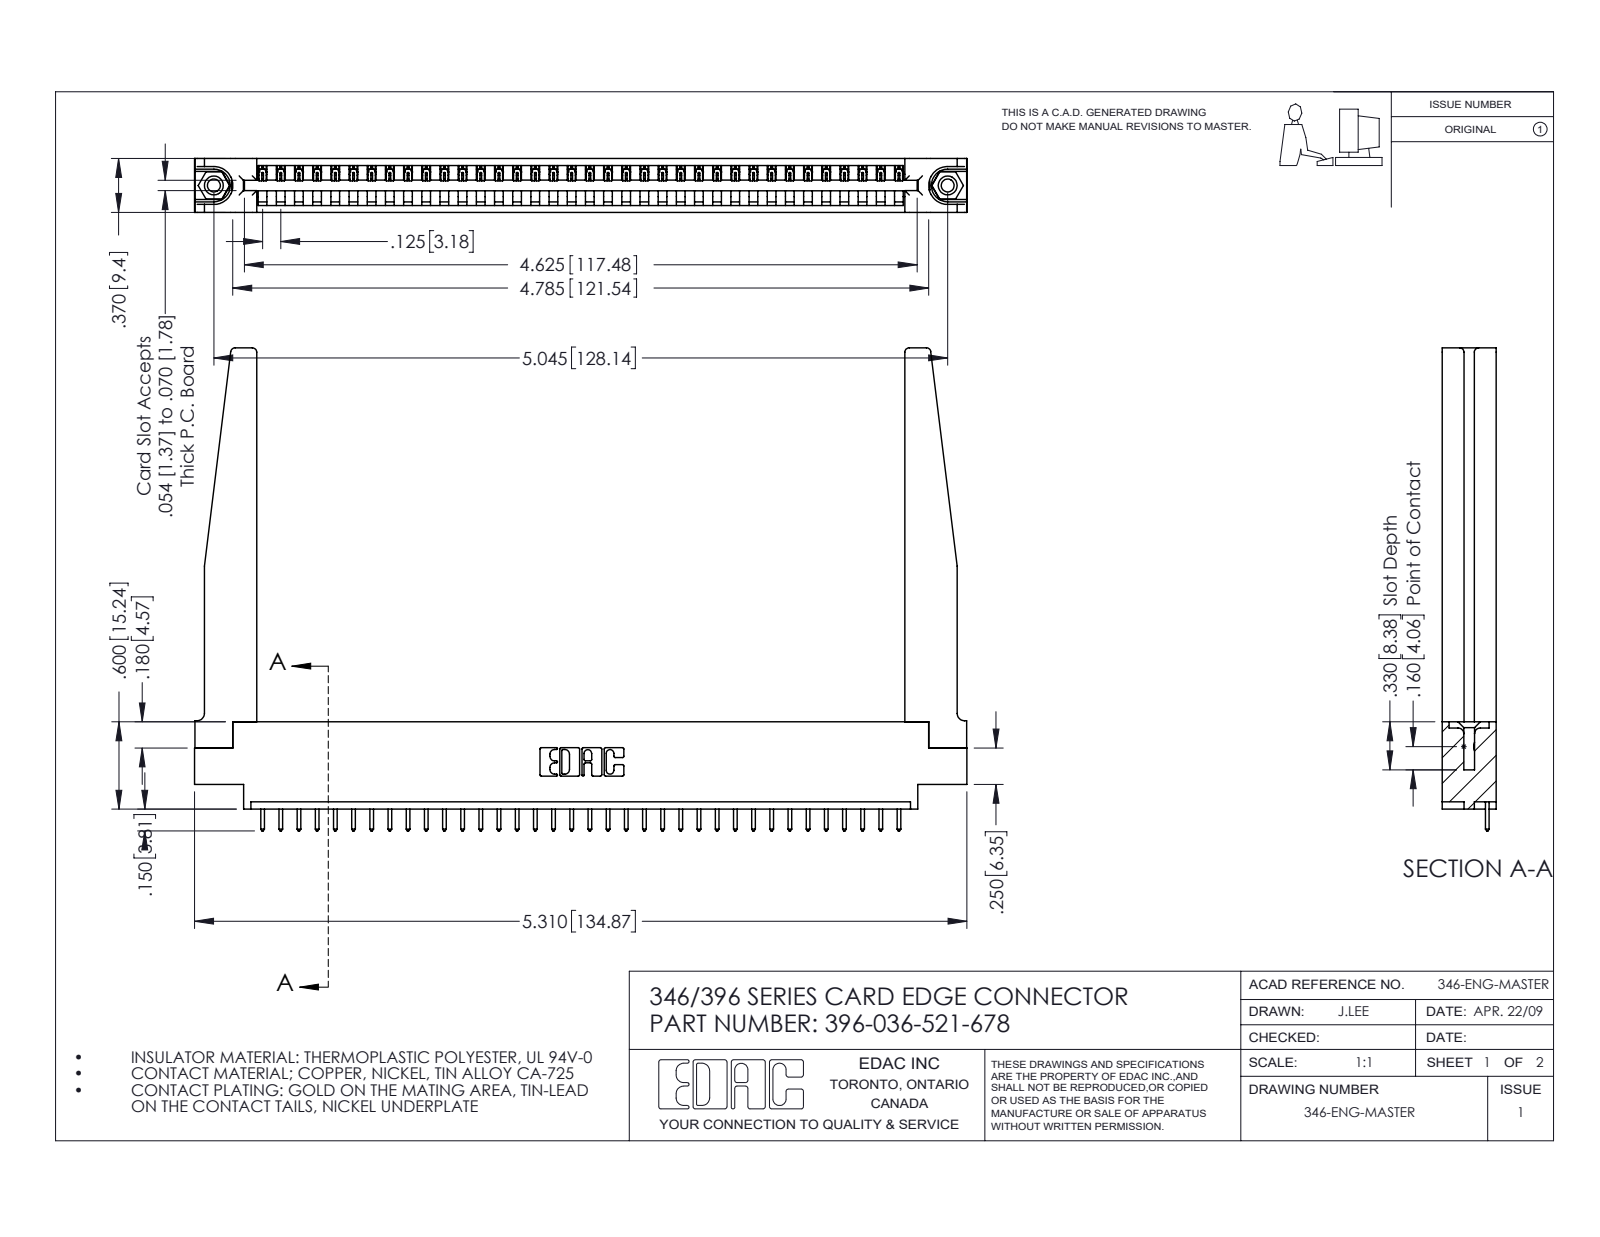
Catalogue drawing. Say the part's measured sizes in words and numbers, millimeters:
The part is named "346-220-078_345-220-078; 346 Part_0.170 Offset - 0.156 Dia-TH; 345-250-001_345-250-001-102; 396-036-521-678 (+1 more)". Its 3-D file was written by "SolidWorks 2016 (CONFIG_CONTROL_DESIGN)". It is 41 solids with 2448 faces: 1662 planar, 734 cylindrical and 52 other. Overall it measures 134.9 by 84.3 by 9.4 millimeters. Its volume is 19 520 cubic millimeters and its surface area 21 990 square millimeters. Round holes: 2 of diameter 2.3, 2 of diameter 3.2, 2 of diameter 4, 1 of diameter 1.6. Round bosses or shafts: 2 of diameter 3.9. Partial cylindrical surfaces (rounded edges, fillets, slot ends): 72 of radius 0.2, 72 of radius 0.3, 22 of radius 0.3, 8 of radius 0.8, 6 of radius 0.2, 6 of radius 0.8, 3 of radius 0.7, 2 of radius 0.8. The main face-to-face distances are 9.4, 1.2, 8.2, 1.8, 3.8, 3.8, 6.4, 7.6, 0.6, 5.6. The hole center spacings are 6.2, 122.8, 128.1.
